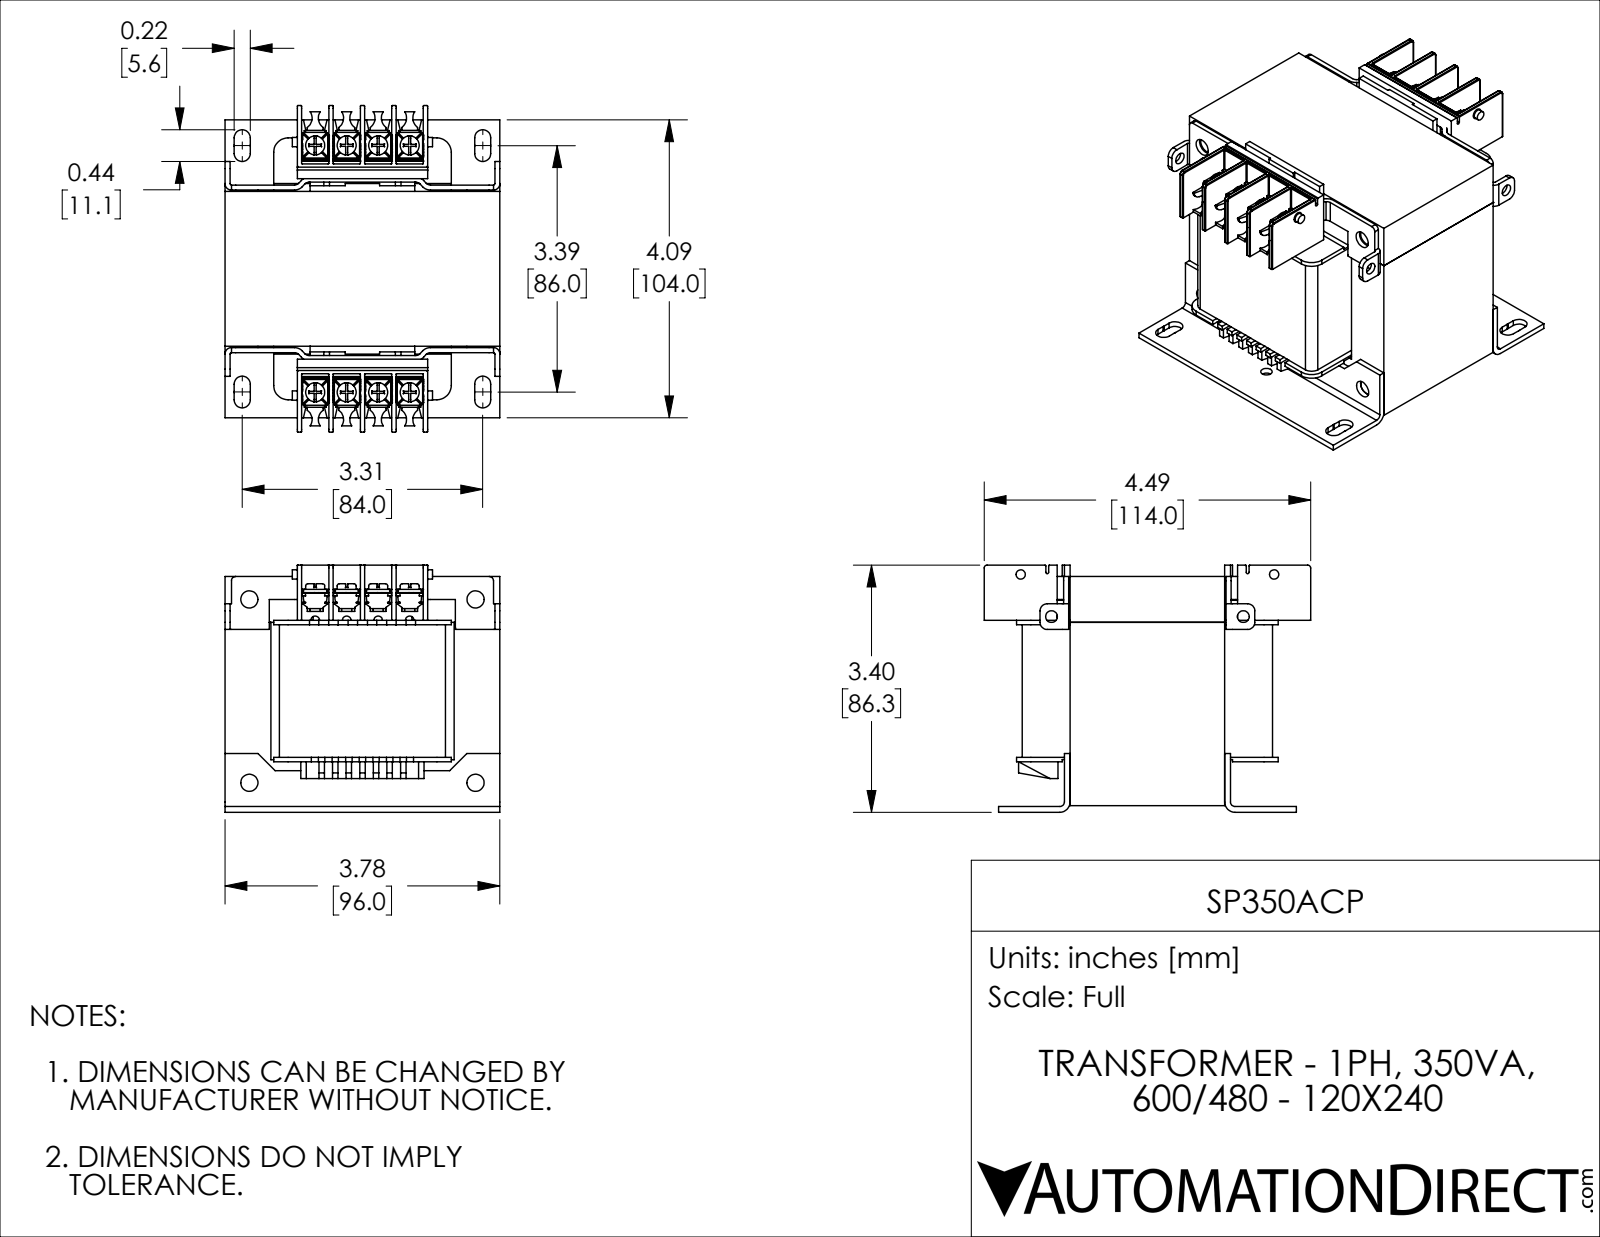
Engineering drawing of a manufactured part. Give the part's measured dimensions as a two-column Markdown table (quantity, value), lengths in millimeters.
| quantity | value |
| --- | --- |
| part name | SP350ACP |
| STEP written by | SolidWorks 2018 (AUTOMOTIVE_DESIGN) |
| units | millimeters |
| bodies | 41 solids, 3229 faces (1997 planar, 934 cylindrical, 298 other) |
| overall size | 114 × 96 × 86.3 |
| volume | 520 000 mm³ |
| surface area | 138 000 mm² |
| round holes (diameter × count) | 4 × 10, 2.7 × 8, 3.5 × 8, 6 × 4, 4.1 × 2 |
| round bosses / shafts (diameter × count) | 6.7 × 8, 6.1 × 8, 4.3 × 8, 2.8 × 8, 3.3 × 2 |
| partial cylindrical surfaces (radius × count) | 0.3 × 62, 0.1 × 52, 0.3 × 42, 0.7 × 32, 4 × 16, 0.9 × 12, 1.7 × 12, 2 × 10 |
| main face-to-face distances | 16, 64, 80, 54, 32, 77, 19, 48, 2, 31.6 |
| hole center spacings | 11, 22, 86.6, 33, 86, 88.7, 86.4, 86.9 |
